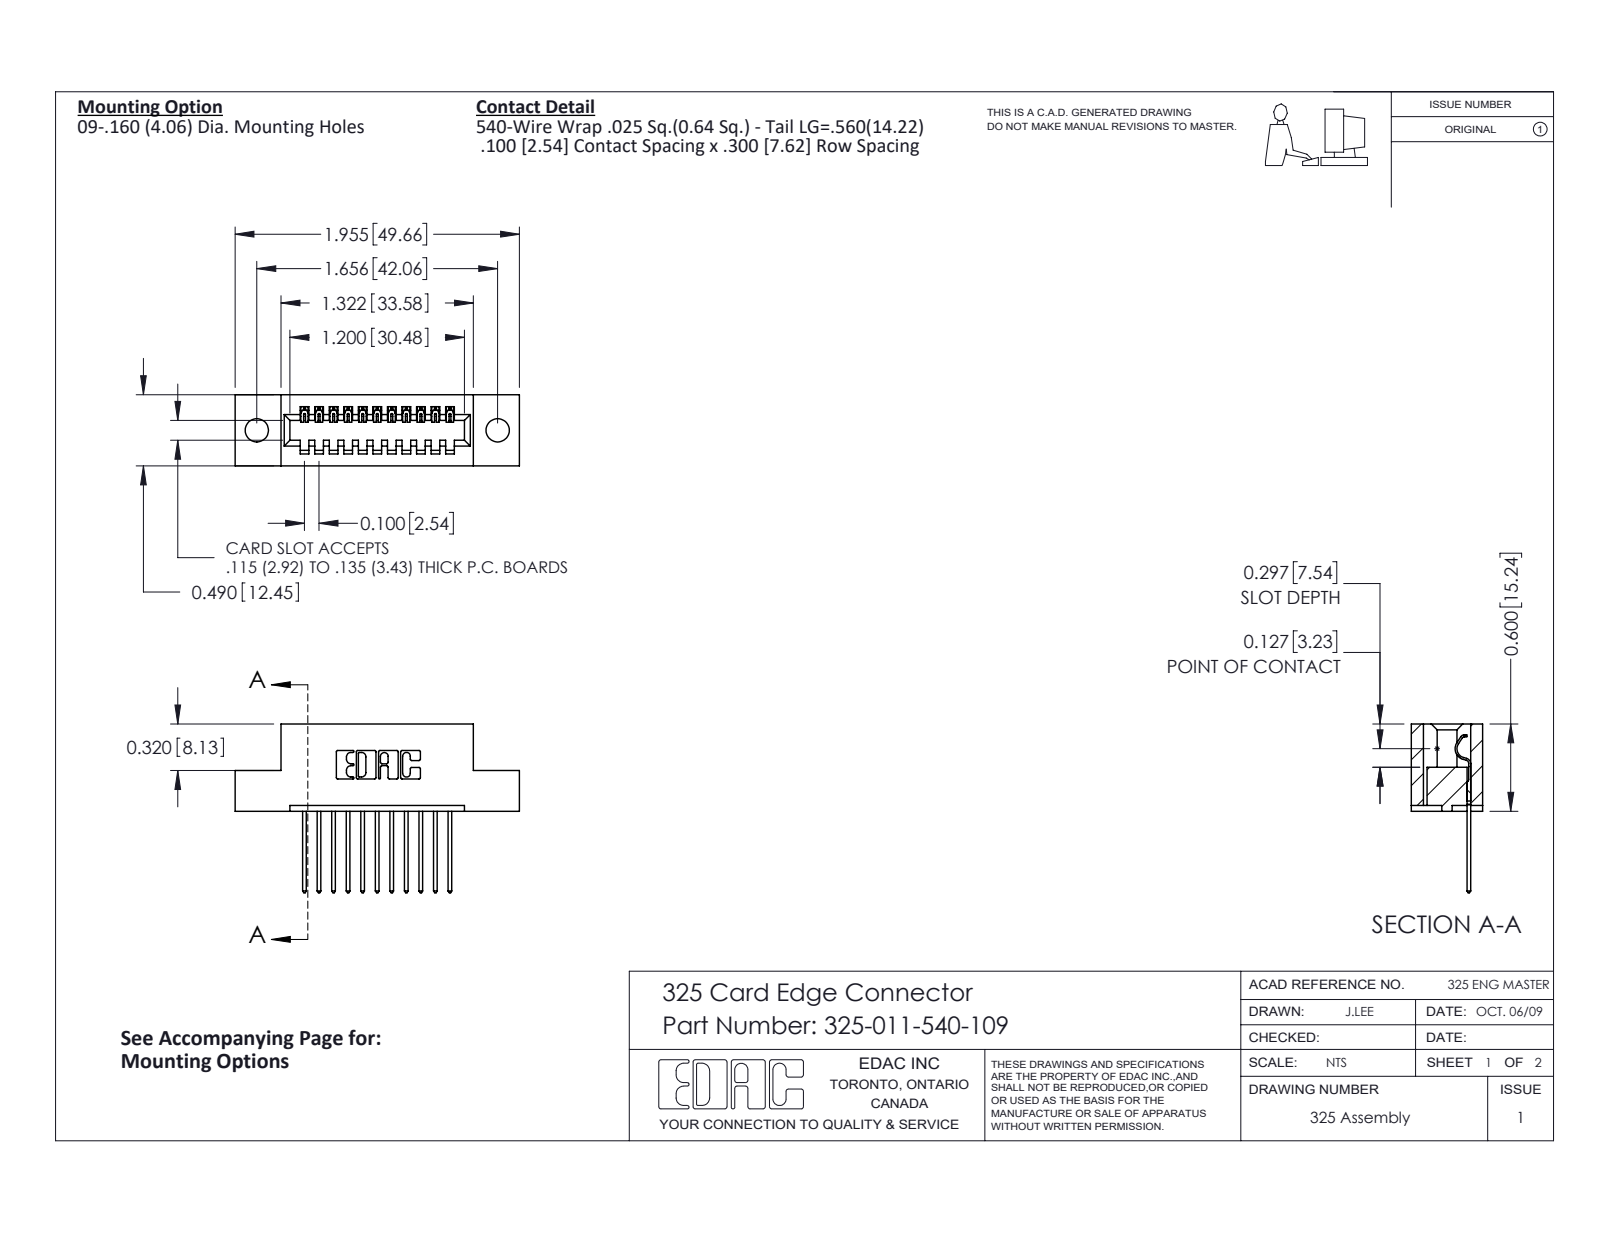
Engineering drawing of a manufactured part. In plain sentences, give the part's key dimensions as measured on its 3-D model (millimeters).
The part is named "325-292-001_325-293-140; 325-011-540-109; 325 Part_.160 TH". Its 3-D file was written by "SolidWorks 2016 (CONFIG_CONTROL_DESIGN)". It is 12 solids with 752 faces: 532 planar, 220 cylindrical and 0 other. Overall it measures 49.7 by 29.5 by 12.4 millimeters. Its volume is 5 850 cubic millimeters and its surface area 5 865 square millimeters. Round holes: 2 of diameter 4.1. Partial cylindrical surfaces (rounded edges, fillets, slot ends): 22 of radius 0.2, 22 of radius 0.3, 22 of radius 0.3, 6 of radius 0.2, 6 of radius 0.8, 3 of radius 0.7, 1 of radius 0.4, 1 of radius 0.6. The main face-to-face distances are 7.6, 2.1, 10.3, 12.4, 1, 2.5, 5.1, 15.2, 2.7, 9.7. The hole center spacings are 42.1.
